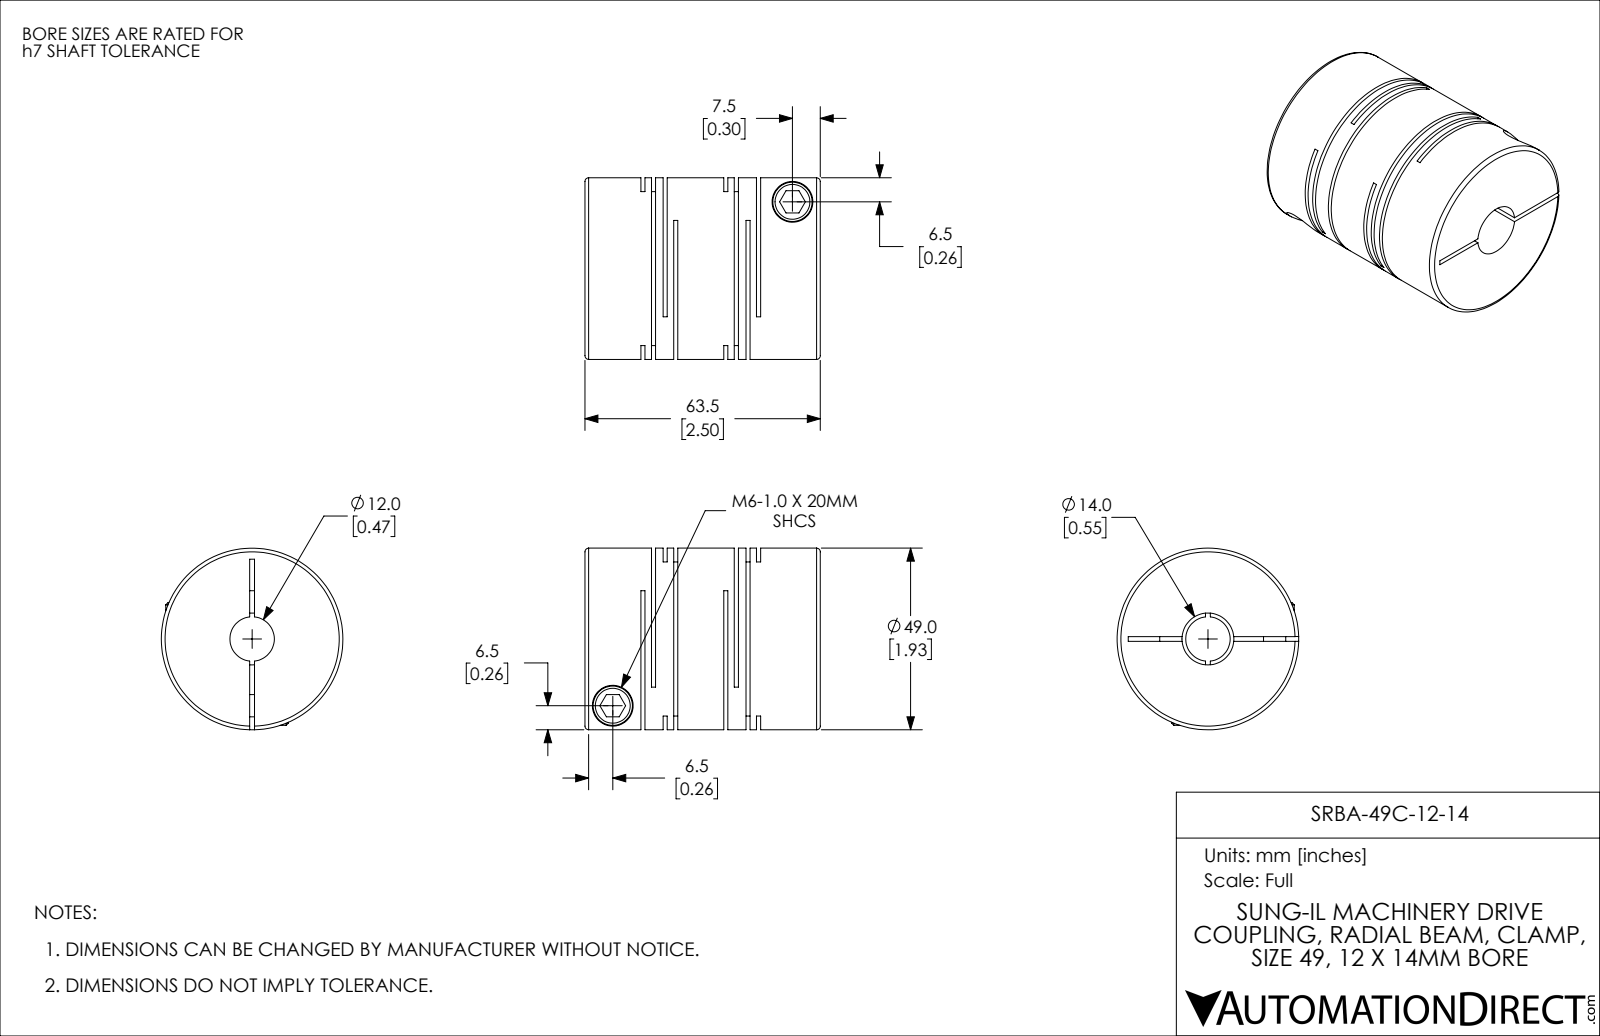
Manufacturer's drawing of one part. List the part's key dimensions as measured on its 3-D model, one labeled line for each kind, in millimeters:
Part name (STEP PRODUCT): SRBA-49C-12-14
STEP written by: SolidWorks 2021 (CONFIG_CONTROL_DESIGN)
Units: millimetres
Bodies: 1 solid, 114 faces (60 planar, 42 cylindrical, 12 other)
Overall size (bounding box): 63.5 × 49 × 49
Volume: 95 327 mm³ · Surface area: 40 208 mm²
Round holes (diameter × count): ⌀6 ×2, ⌀11 ×2, ⌀12 ×1, ⌀14 ×1
Round bosses / shafts (diameter × count): ⌀10.6 ×2, ⌀49 ×1
Main face-to-face distances: 6, 1.1, 2.85, 22.35, 1.75, 4.9, 21.25, 3.15, 19.5, 16.35
